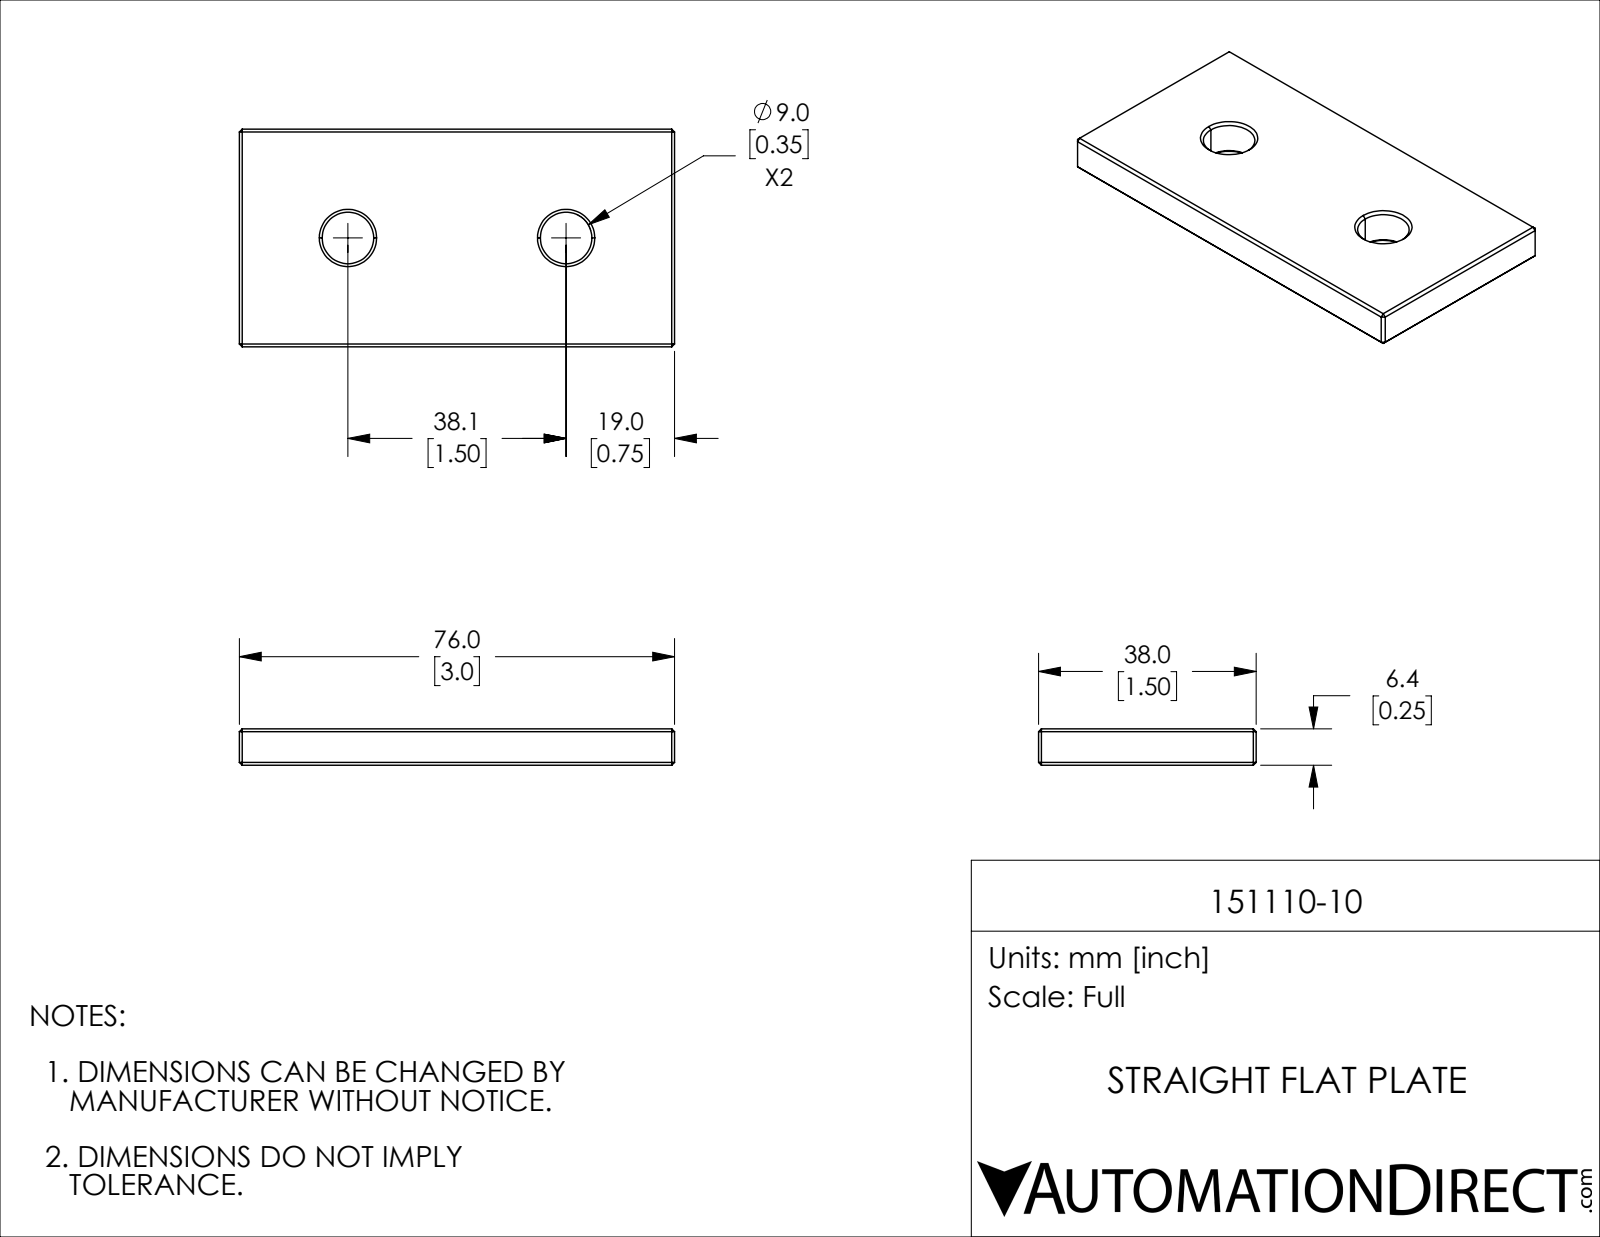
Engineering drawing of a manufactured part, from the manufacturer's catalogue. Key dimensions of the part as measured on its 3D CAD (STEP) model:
Part name (STEP PRODUCT): 151110-10
STEP written by: SolidWorks 2024 (CONFIG_CONTROL_DESIGN)
Units: millimetres
Bodies: 1 solid, 38 faces (26 planar, 4 cylindrical, 8 other)
Overall size (bounding box): 76 × 38 × 6.35
Volume: 17 457 mm³ · Surface area: 7 155 mm²
Round holes (diameter × count): ⌀9 ×2
Main face-to-face distances: 6.35, 38, 76, 30.65, 57.51, 79.9, 68.29
Hole centre spacings: 38.1
